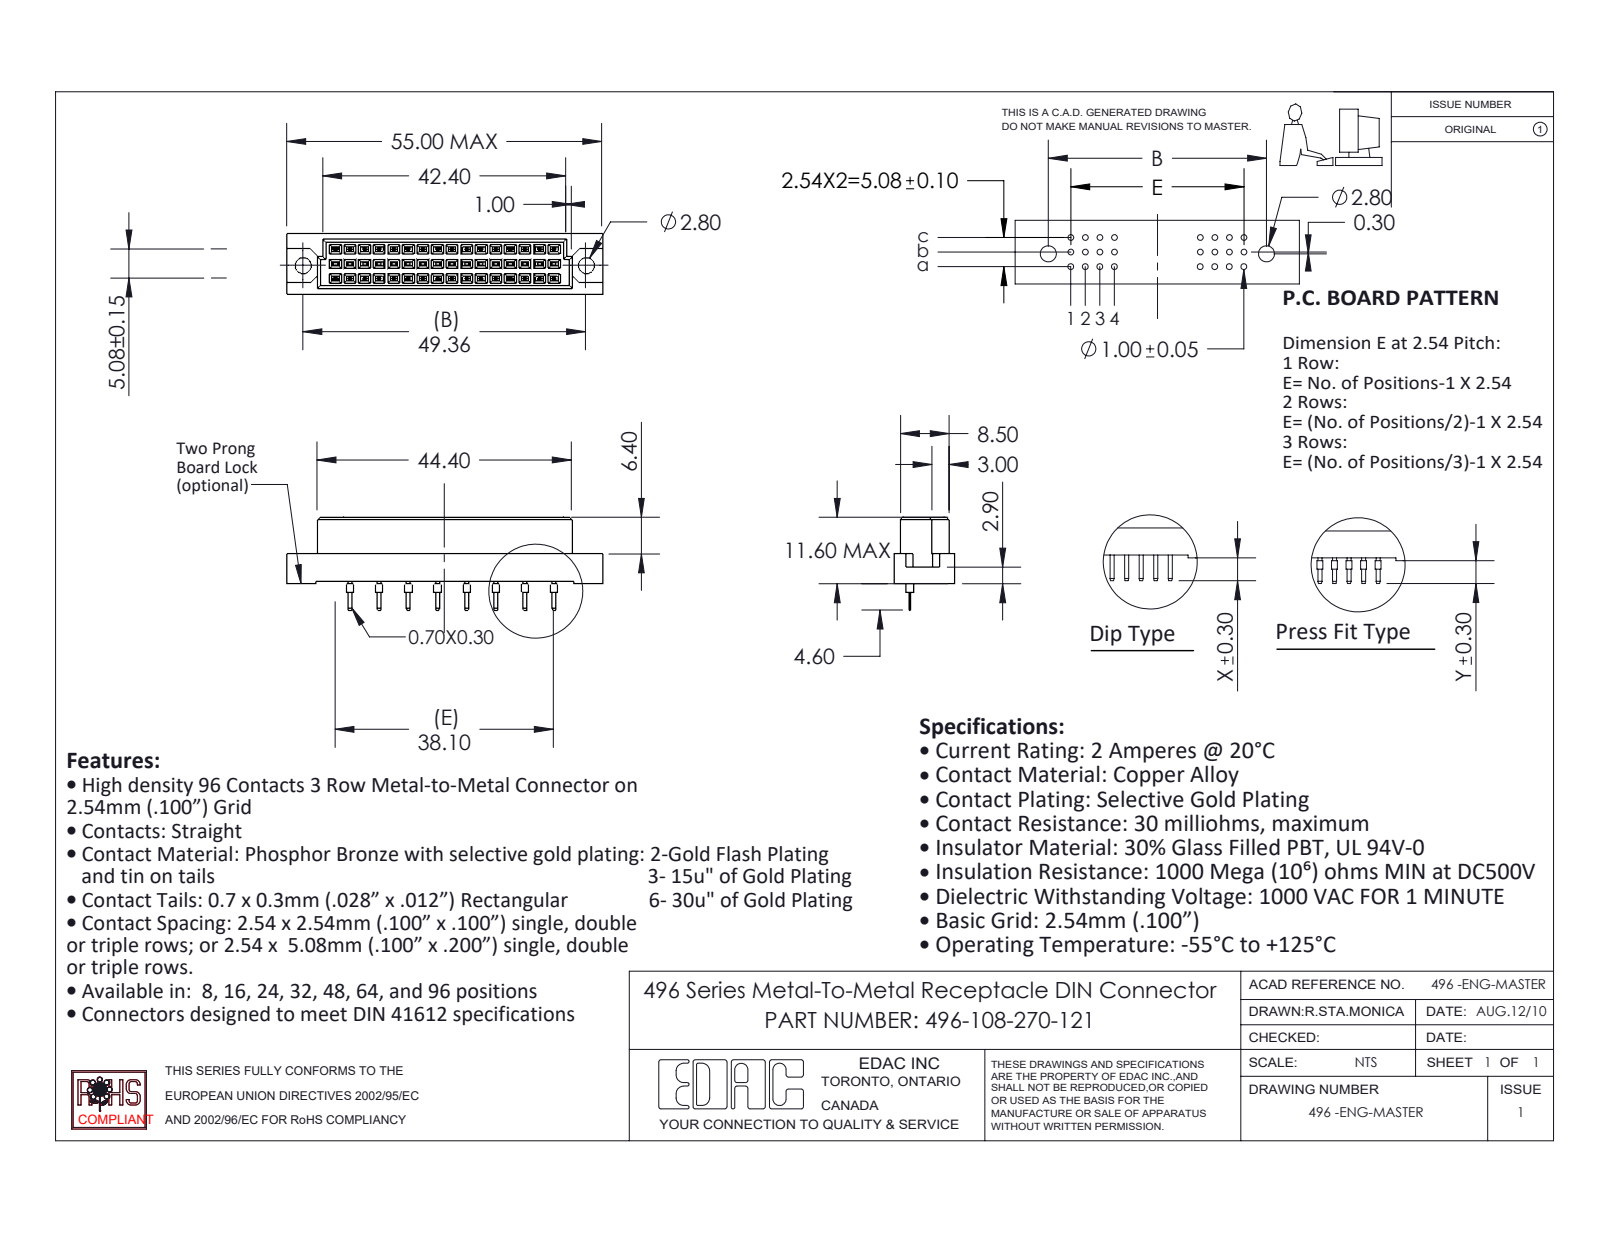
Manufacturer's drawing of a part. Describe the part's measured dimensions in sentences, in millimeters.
The part is named "496-290_70; 496-108-270-121; 496 Part_48". Its 3-D file was written by "SolidWorks 2020 (CONFIG_CONTROL_DESIGN)". It is 9 solids with 810 faces: 790 planar, 20 cylindrical and 0 other. Overall it measures 55 by 16.2 by 10.6 millimeters. Its volume is 4 612 cubic millimeters and its surface area 4 389 square millimeters. Round holes: 2 of diameter 2.8. Round bosses or shafts: 8 of diameter 1. The main face-to-face distances are 2.54, 5.08, 1.05, 9.55, 0.81, 10.6, 3.35, 1.73, 8.5, 0.56. The hole center spacings are 49.36.
